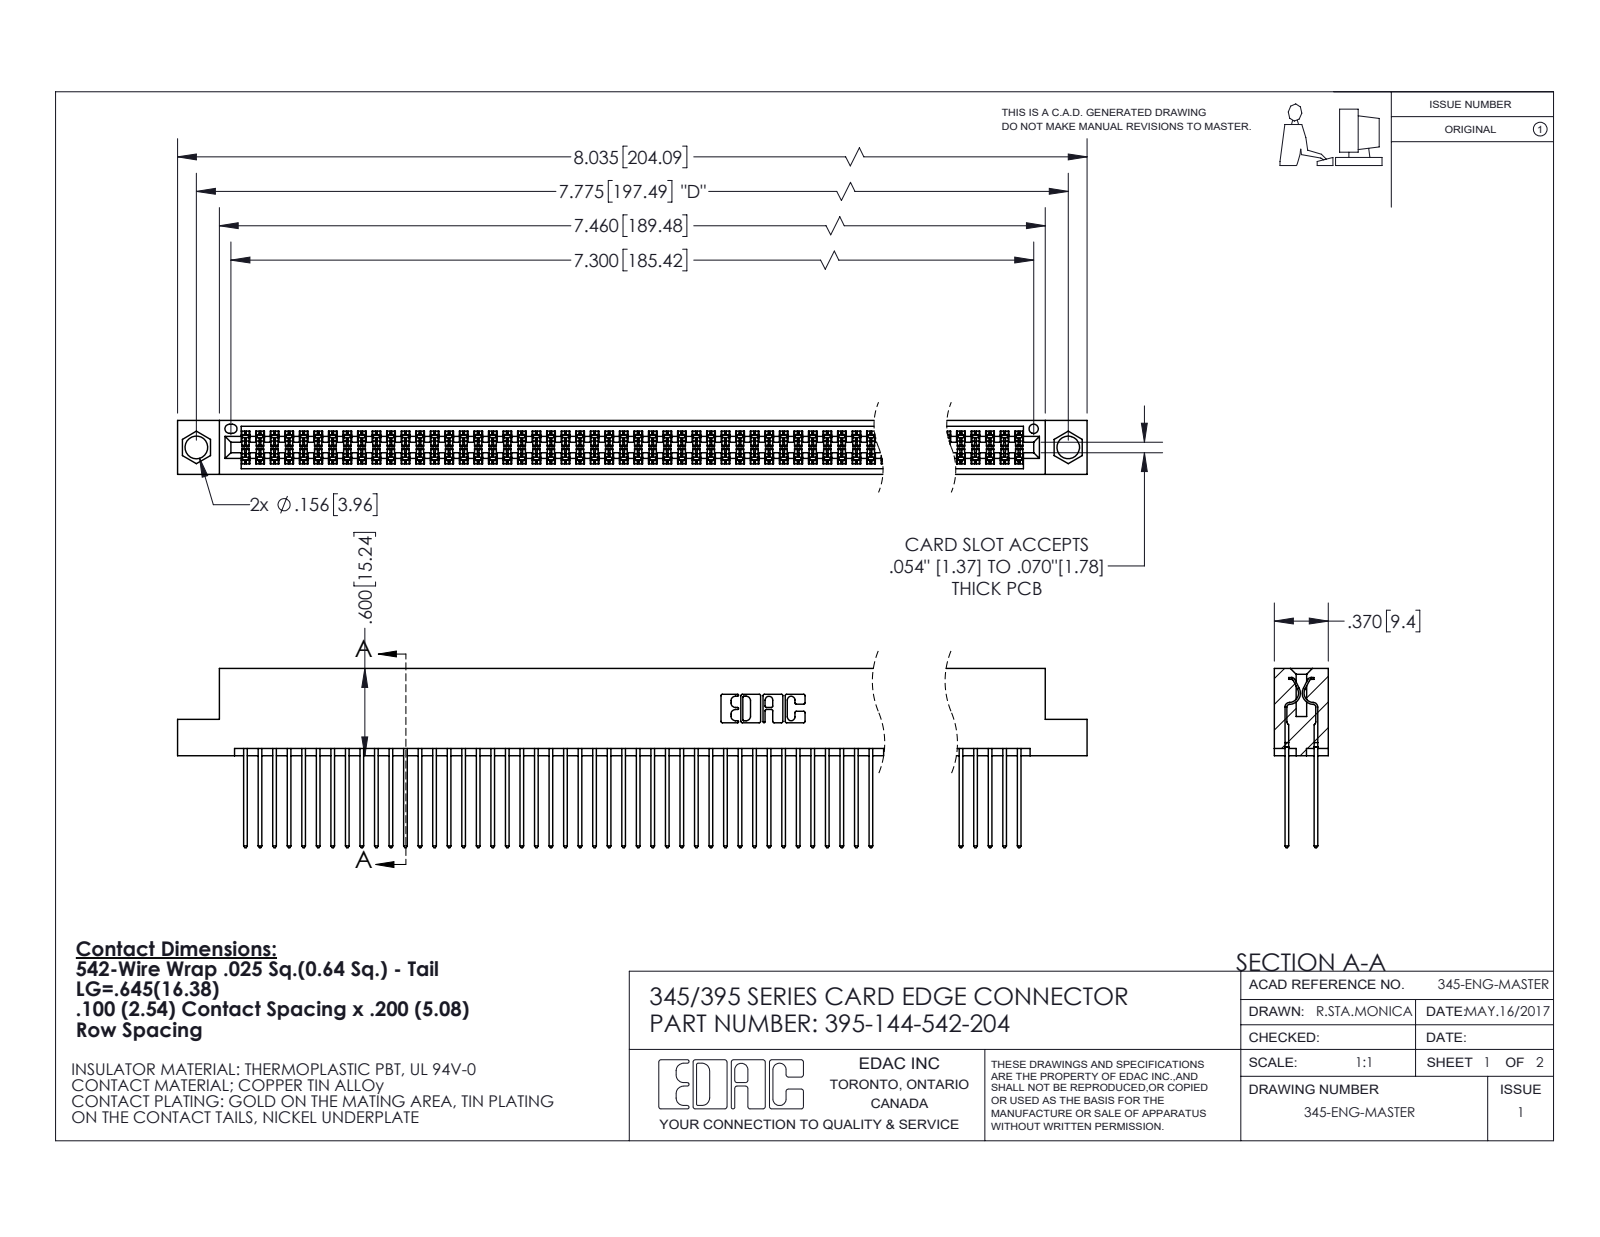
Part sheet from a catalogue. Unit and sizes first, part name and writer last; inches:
Units: inches
Overall size (bounding box): 8.035 × 1.232 × 0.37
Round holes (diameter × count): ⌀0.156 ×2, ⌀0.064 ×1
Partial cylindrical surfaces — rounded edges, fillets, slot ends (radius × count): R0.006 ×216, R0.01 ×144, R0.01 ×22, R0.007 ×6, R0.031 ×6, R0.026 ×3, R0.014 ×2, R0.019 ×2
Main face-to-face distances: 0.072, 0.298, 0.2, 0.098, 0.272, 0.025, 0.225, 0.37, 0.175, 0.149
Hole centre spacings: 0.27, 7.539, 7.775
Volume: 1.261 in³ · Surface area: 52.89 in²
Bodies: 145 solids, 7340 faces (4846 planar, 2494 cylindrical, 0 other)
Part name (STEP PRODUCT): 345 Part_Flush Mounting Lugs - 0.156 Dia-TI; 395-144-542-204; 345-292-001_345-293-142
STEP written by: SolidWorks 2020 (CONFIG_CONTROL_DESIGN)
